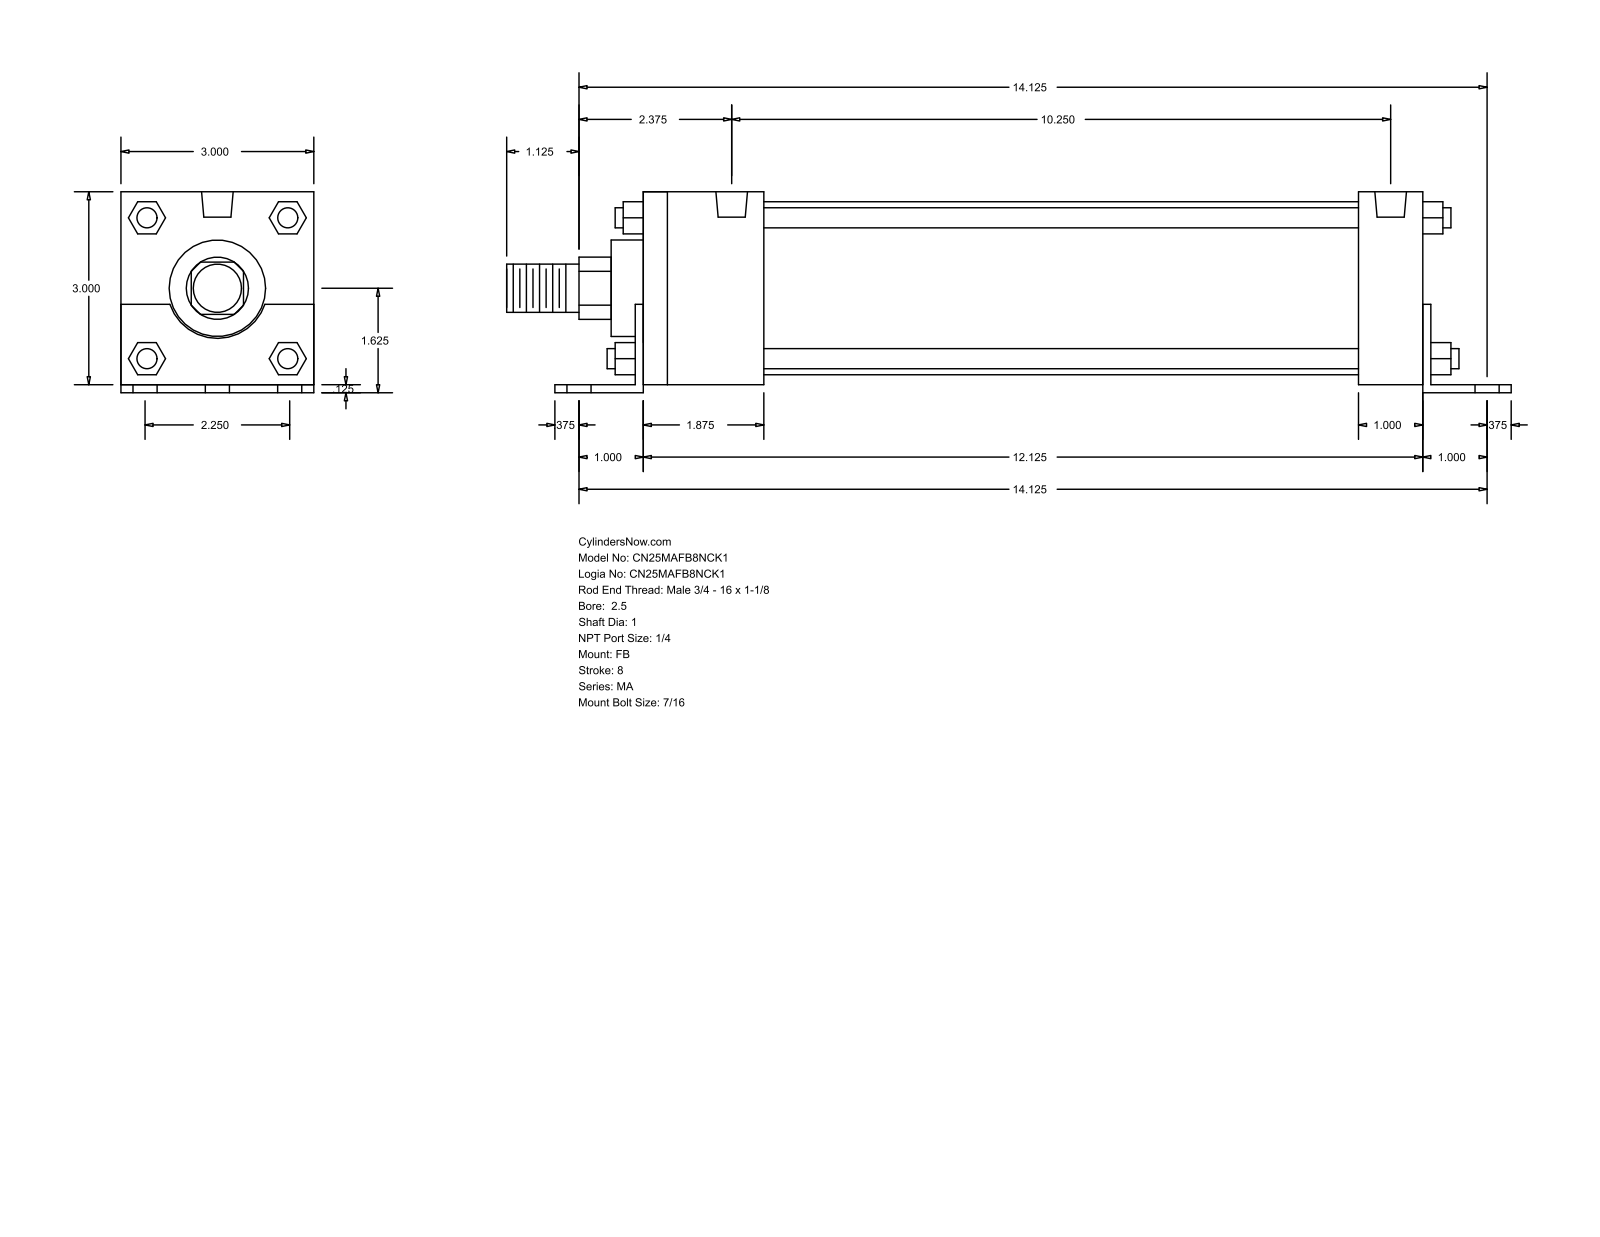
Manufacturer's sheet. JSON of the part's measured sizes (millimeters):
{"part_name": "MA_FB__0250_1", "step_written_by": "GSSL Pune (CONFIG_CONTROL_DESIGN)", "units": "millimeters", "bodies": {"solids": 0, "faces": 140, "planar": 105, "cylindrical": 35, "other": 0}, "overall_size": [396.88, 79.38, 76.2], "round_holes": [[11.11, 6], [7.94, 4], [12.49, 2]], "round_bosses_or_shafts": [[7.94, 4], [68.33, 1], [38.1, 1], [25.4, 1], [19.05, 1]], "partial_cylinders_radius": [[12.29, 1], [19.81, 1]], "face_to_face_distances": [76.2, 3.17, 79.37, 311.15, 307.98, 12.7, 28.57, 25.4, 50.8, 47.63], "hole_center_spacings": [28.57, 359.91, 358.77, 47.61, 57.14, 66.75, 260.35, 299.8]}
